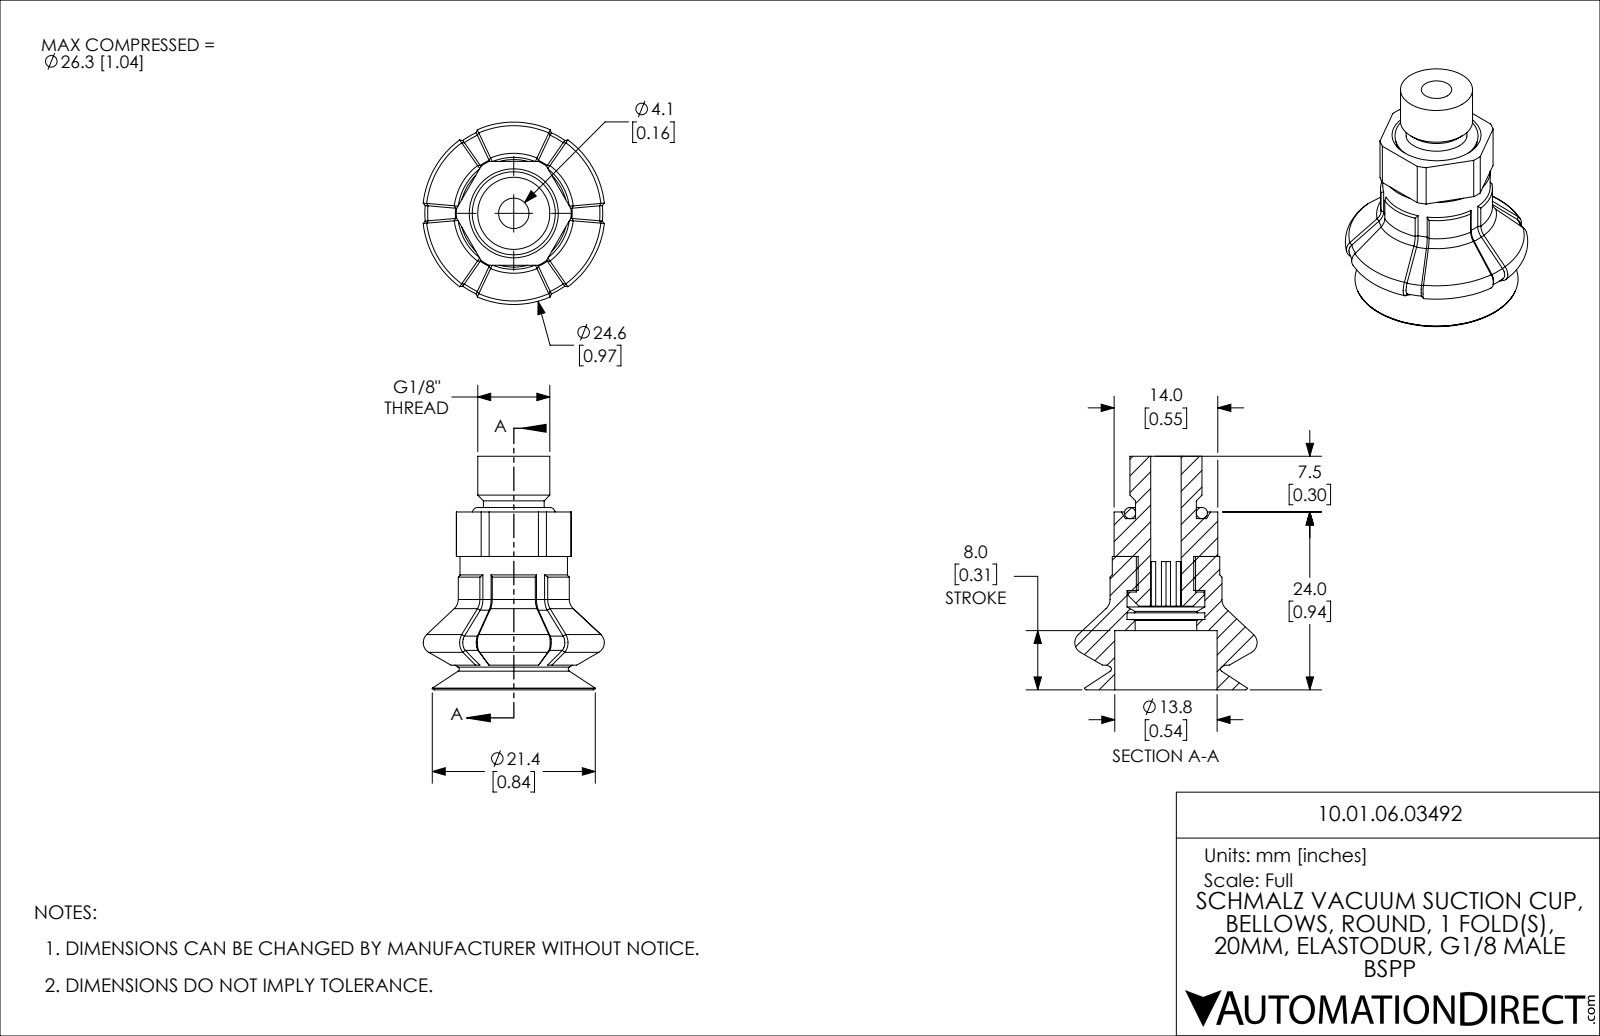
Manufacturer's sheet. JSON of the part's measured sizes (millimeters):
{"part_name": "10.01.06.03492", "step_written_by": "SolidWorks 2021 (CONFIG_CONTROL_DESIGN)", "units": "millimeters", "bodies": {"solids": 3, "faces": 228, "planar": 53, "cylindrical": 35, "other": 140}, "overall_size": [31.5, 24.6, 24.44], "volume_mm3": 4616, "surface_area_mm2": 4146, "round_holes": [[4.1, 1], [7.5, 1], [8.3, 1], [10.5, 1], [13.8, 1]], "round_bosses_or_shafts": [[14.5, 1], [10.3, 1], [9.73, 1], [8.2, 1], [8, 1]], "partial_cylinders_radius": [[7.55, 1], [7.75, 1]], "face_to_face_distances": [18, 14, 8, 10, 0.9, 31.5, 23.5, 13.5, 12.7, 6]}
